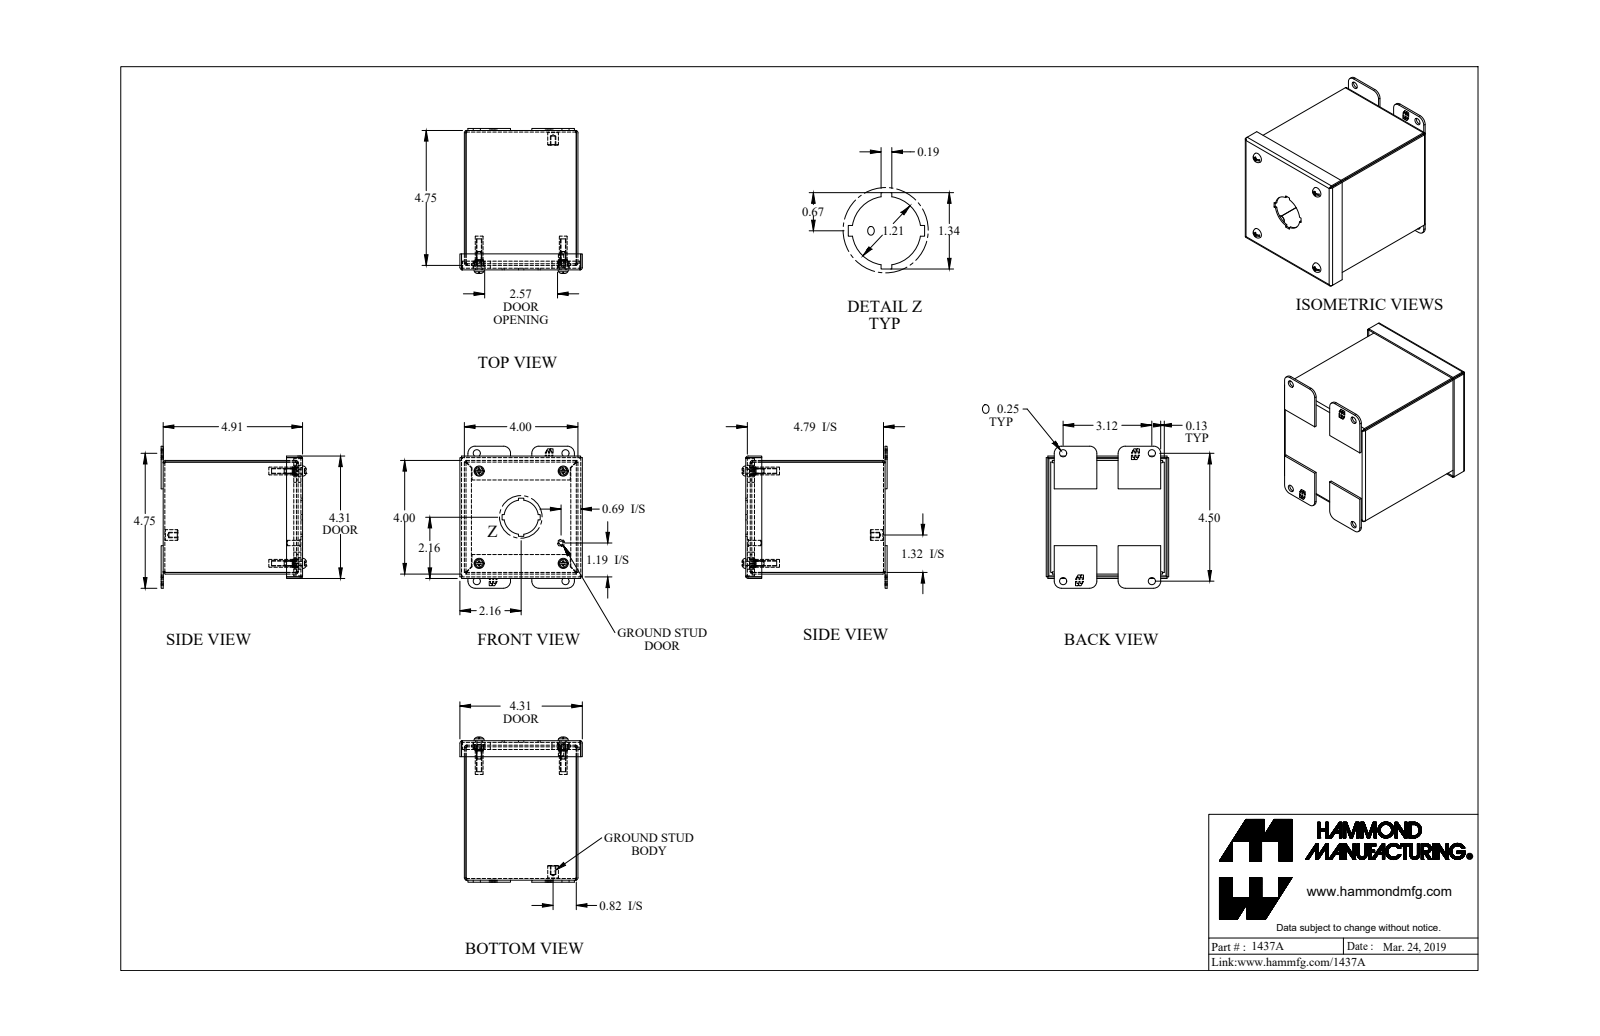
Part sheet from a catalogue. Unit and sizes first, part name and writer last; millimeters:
Units: millimetres
Overall size (bounding box): 129.7 × 127 × 109.5
Round holes (diameter × count): ⌀6.4 ×8, ⌀4 ×4, ⌀10.3 ×4, ⌀4 ×1, ⌀30.7 ×1
Round bosses / shafts (diameter × count): ⌀9.9 ×4, ⌀7 ×4, ⌀4.8 ×4, ⌀3.8 ×4, ⌀9.5 ×1, ⌀6.4 ×1, ⌀4.8 ×1
Partial cylindrical surfaces — rounded edges, fillets, slot ends (radius × count): R0.7 ×12, R2.2 ×12, R6.4 ×8, R4.1 ×4, R4.3 ×4
Main face-to-face distances: 1.4, 100.2, 123.2, 101.6, 98.7, 124.6, 4, 104.1, 121.7, 4
Hole centre spacings: 82.6, 78.9, 111.7, 111.7, 16, 69.6, 75.2, 78.9
Volume: 152 000 mm³ · Surface area: 190 300 mm²
Bodies: 21 solids, 651 faces (447 planar, 148 cylindrical, 56 other)
Part name (STEP PRODUCT): 1437A_Default
STEP written by: SolidWorks 2019 (CONFIG_CONTROL_DESIGN)
